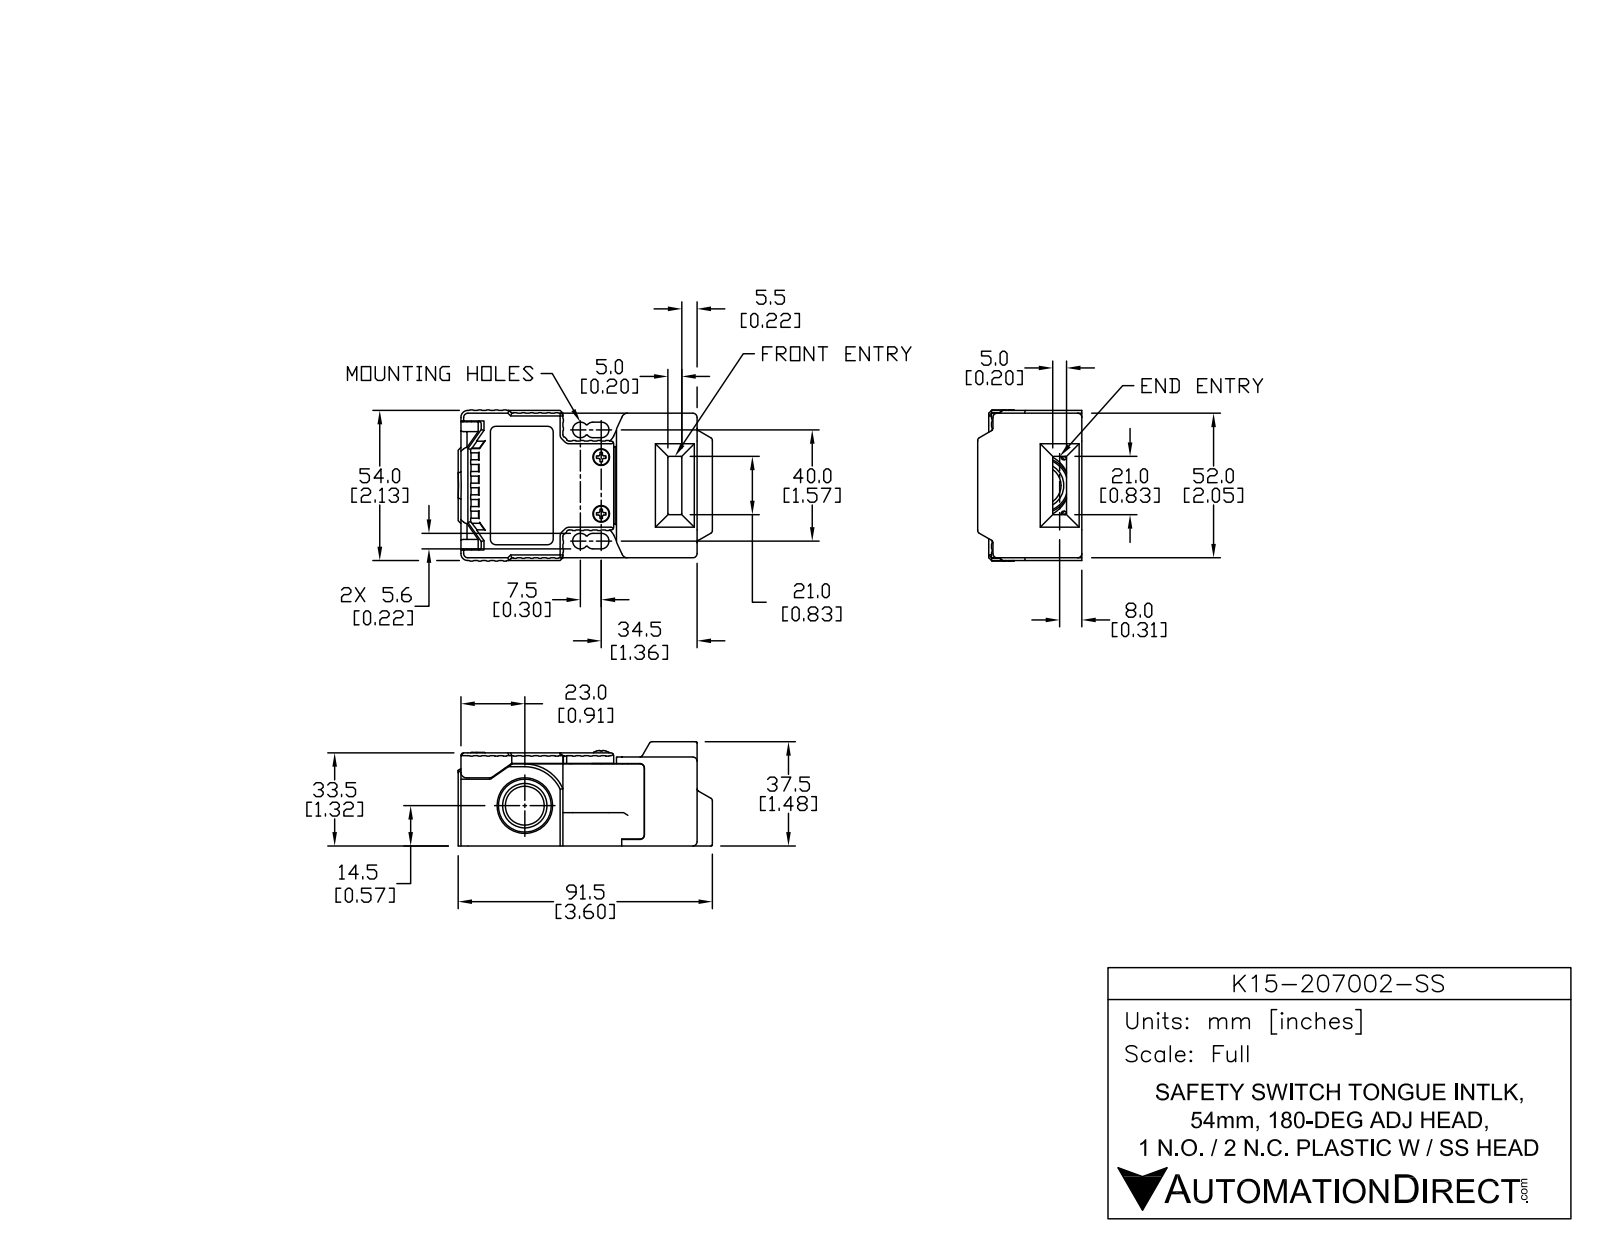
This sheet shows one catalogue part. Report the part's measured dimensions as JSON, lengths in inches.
{"part_name": "K-15-207002-SS", "step_written_by": "SolidWorks 2013 (AUTOMOTIVE_DESIGN)", "units": "inches", "bodies": {"solids": 1, "faces": 308, "planar": 162, "cylindrical": 91, "other": 55}, "overall_size": [3.602, 2.283, 1.476], "volume_in3": 8.515, "surface_area_in2": 36.47, "round_holes": [[0.761, 1], [0.787, 1]], "round_bosses_or_shafts": [[0.22, 2]], "partial_cylinders_radius": [[0.02, 55], [0.11, 6], [0.079, 4], [0.118, 4], [0.157, 3]], "face_to_face_distances": [0.118, 2.165, 1.319, 2.047, 1.26, 0.059, 3.346, 0.217, 1.317, 0.057]}
